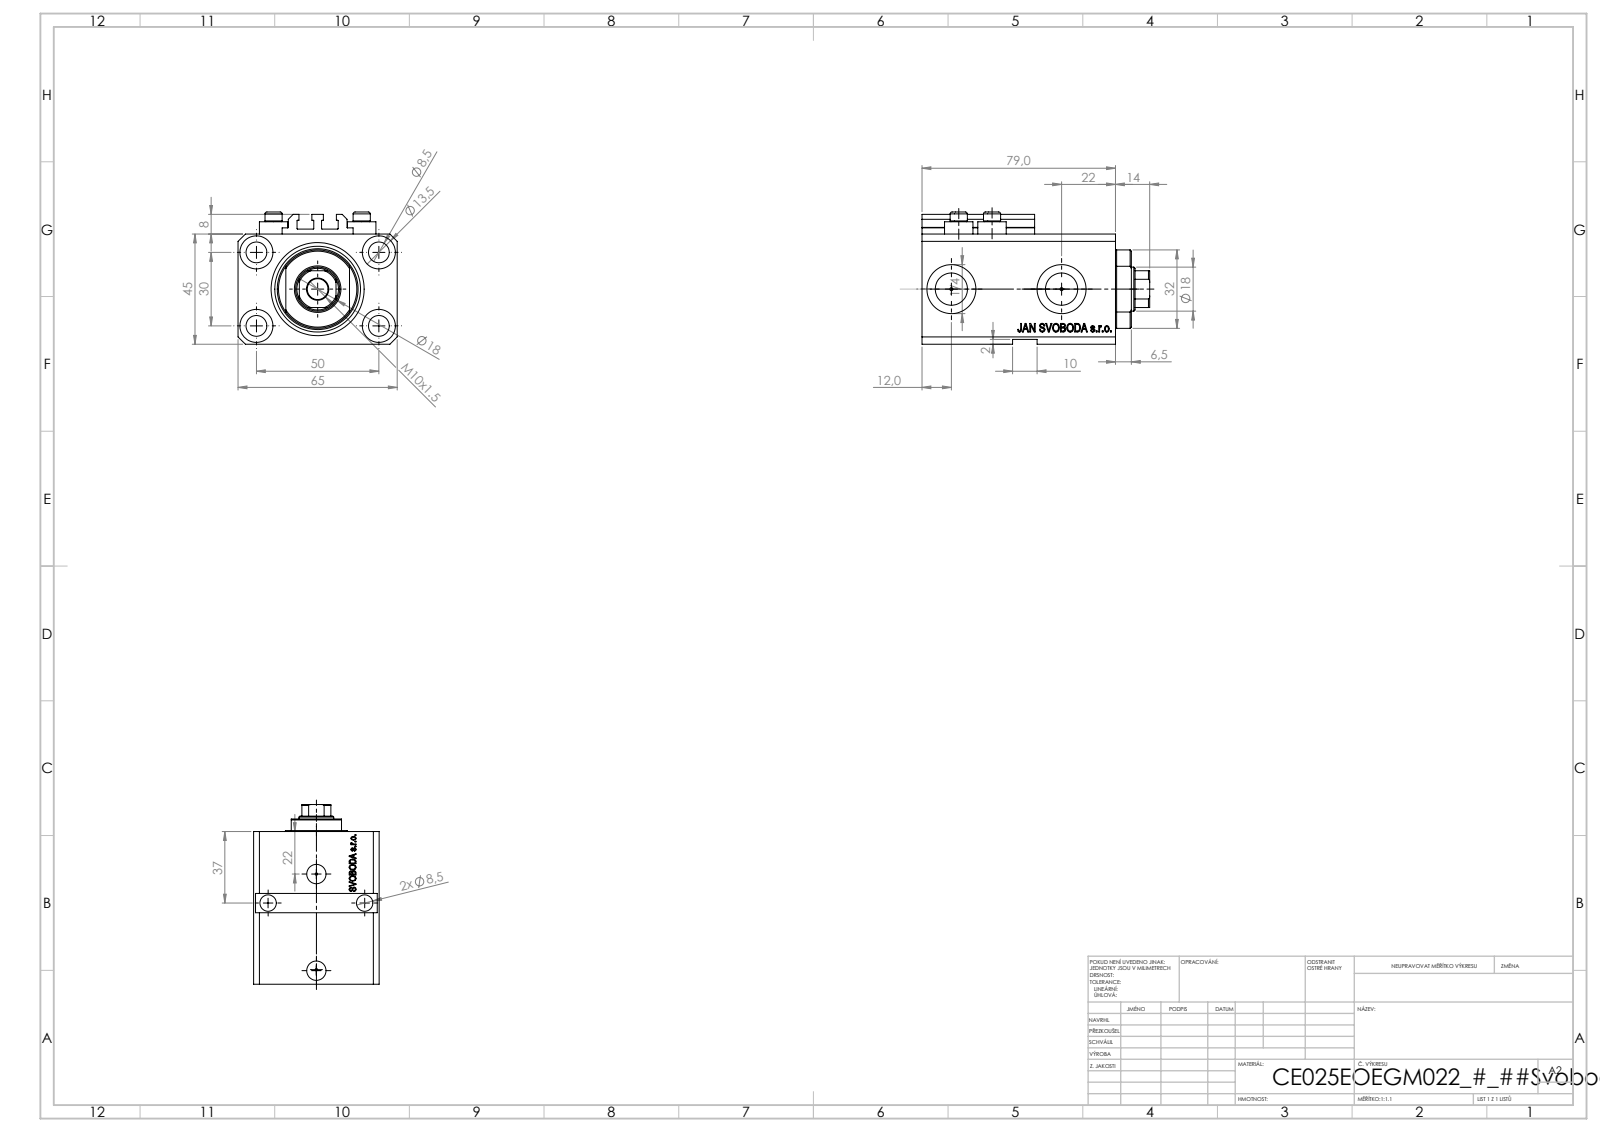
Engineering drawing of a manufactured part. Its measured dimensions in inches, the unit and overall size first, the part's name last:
Units: inches
Overall size (bounding box): 3.661 × 2.559 × 2.126
Round holes (diameter × count): ⌀0.335 ×7, ⌀0.049 ×4, ⌀0.157 ×4, ⌀0.531 ×4, ⌀0.394 ×2, ⌀0.518 ×2, ⌀0.787 ×2, ⌀0.709 ×1, ⌀0.984 ×1, ⌀1.496 ×1
Round bosses / shafts (diameter × count): ⌀0.457 ×4, ⌀0.276 ×4
Partial cylindrical surfaces — rounded edges, fillets, slot ends (radius × count): R0.008 ×10, R0.335 ×1, R0.63 ×1
Main face-to-face distances: 1.772, 2.559, 0.551, 3.11, 0.079, 1.85, 0.118, 0.272, 2.287, 2.839
Hole centre spacings: 1.148, 1.969, 0.535, 0.595, 0.767, 0.776, 1.091, 1.098
Volume: 12.5 in³ · Surface area: 93.46 in²
Bodies: 8 solids, 1067 faces (511 planar, 126 cylindrical, 430 other)
Part name (STEP PRODUCT): V250CE_C_VCP; ALLEN BOLT V250CE; V250CE_E_Body; V250CE_VC_E
STEP written by: SolidWorks 2019 (CONFIG_CONTROL_DESIGN)
